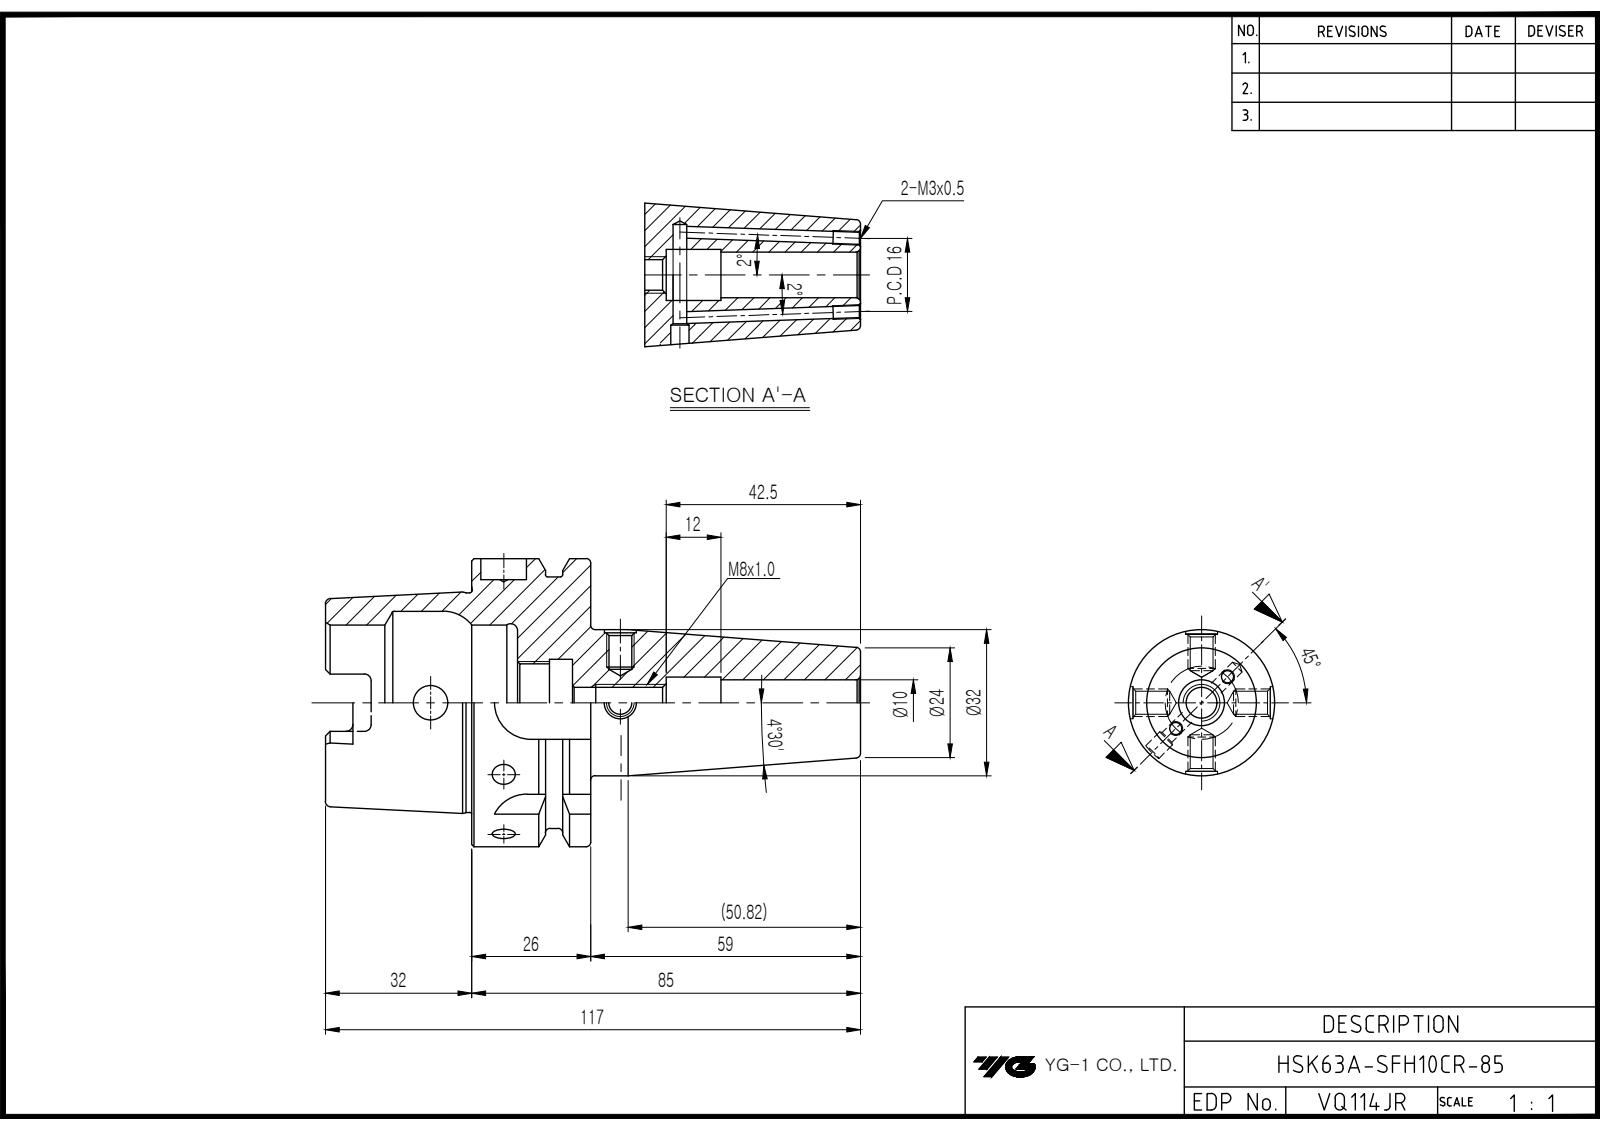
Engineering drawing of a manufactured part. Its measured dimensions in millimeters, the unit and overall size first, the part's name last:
Units: millimetres
Overall size (bounding box): 117 × 63 × 63
Round holes (diameter × count): ⌀2.46 ×2, ⌀10 ×2, ⌀6.92 ×1, ⌀7.5 ×1, ⌀11.2 ×1, ⌀16.92 ×1, ⌀19 ×1, ⌀34 ×1, ⌀40 ×1
Round bosses / shafts (diameter × count): ⌀63 ×1, ⌀55 ×1, ⌀48.04 ×1, ⌀32 ×1
Partial cylindrical surfaces — rounded edges, fillets, slot ends (radius × count): R1.5 ×6, R2.88 ×4, R8 ×4
Main face-to-face distances: 26, 10, 16, 32, 42, 58, 22, 4, 12, 53
Volume: 115 027 mm³ · Surface area: 29 556 mm²
Bodies: 1 solid, 119 faces (42 planar, 35 cylindrical, 42 other)
Part name (STEP PRODUCT): LO-HSK63A-SFH10CR-85
STEP written by: Autodesk Inventor 2022 (AUTOMOTIVE_DESIGN)
